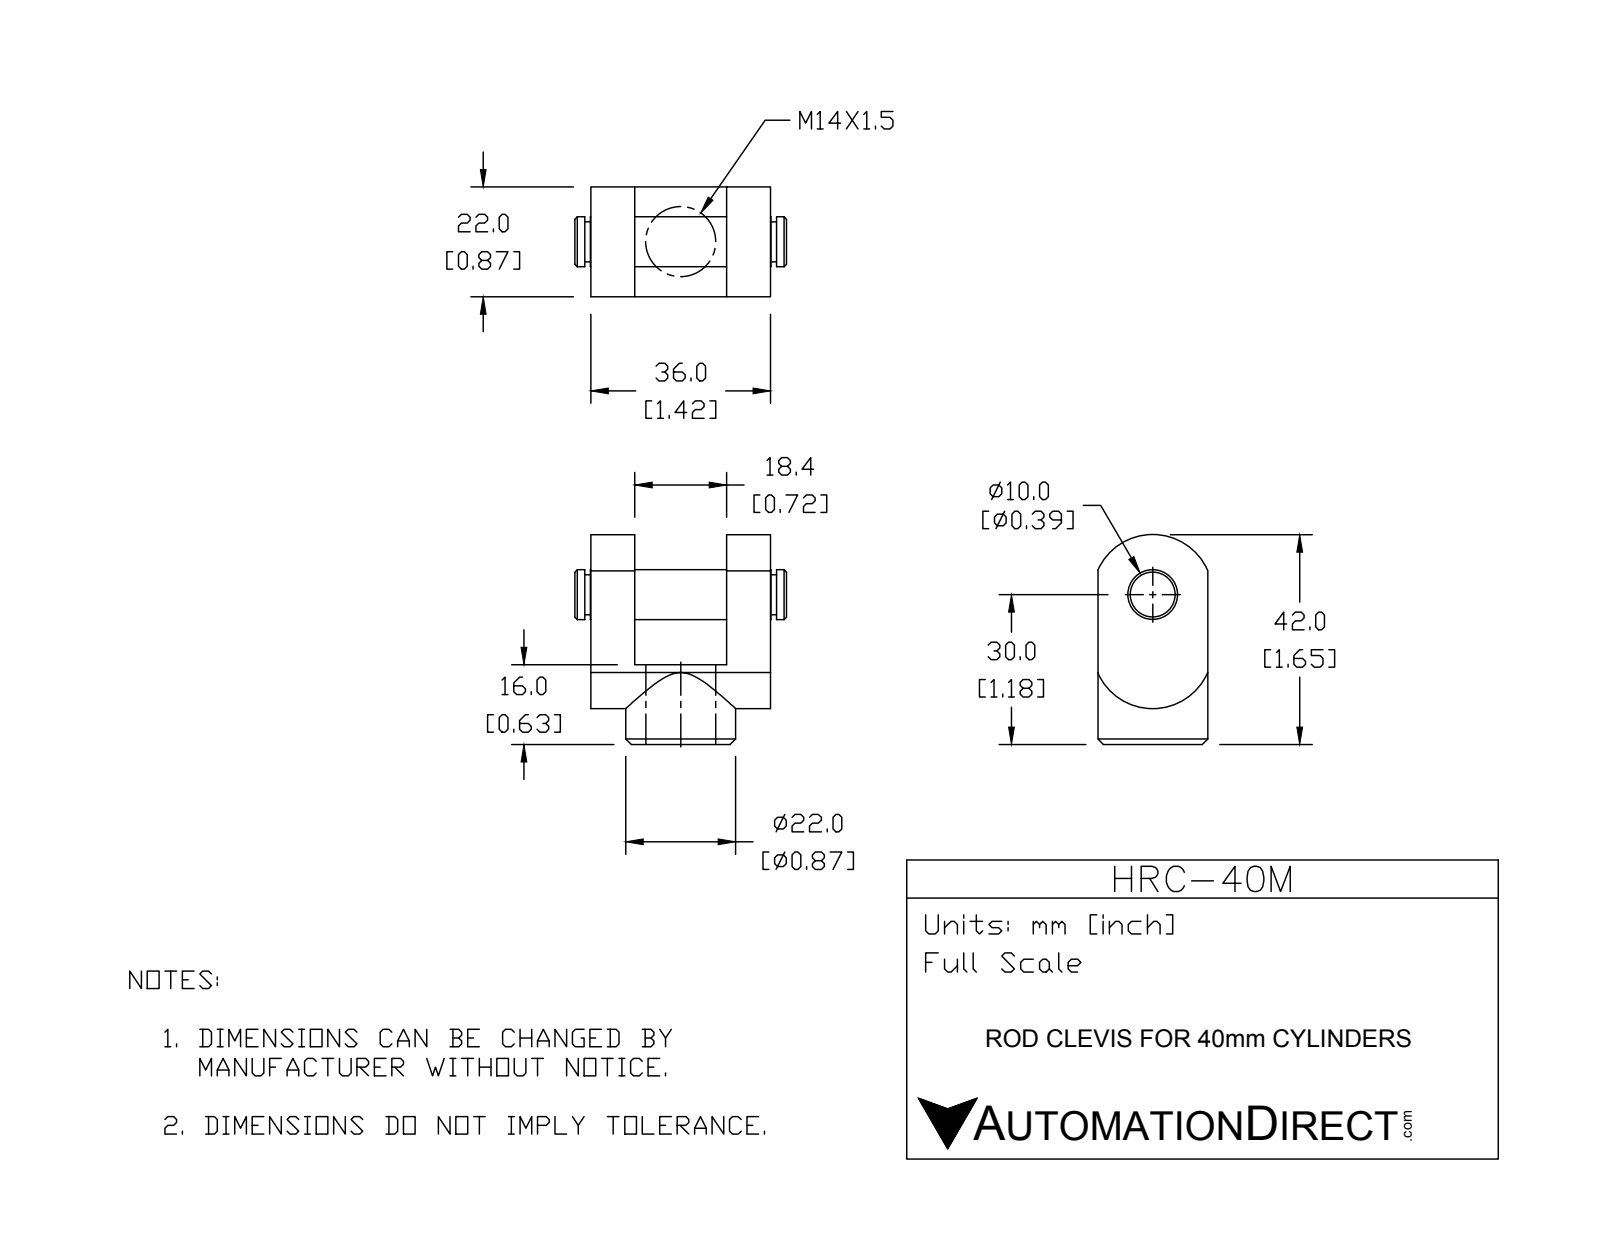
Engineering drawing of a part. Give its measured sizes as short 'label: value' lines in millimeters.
name: HRC-40M
written by: SolidWorks 2015 (CONFIG_CONTROL_DESIGN)
unit: mm
bodies: 2 solids, 46 faces (14 planar, 22 cylindrical, 10 other)
size: 42.4 × 42 × 22
volume: 17 803 mm³; area: 7 848 mm²
holes: 1× ⌀12.5
bosses: 1× ⌀22, 1× ⌀10, 1× ⌀8
rounds: 2× R12
face distances: 8.8, 27.2, 36, 18.4, 22, 16, 3.2, 12, 30.4, 39.2
